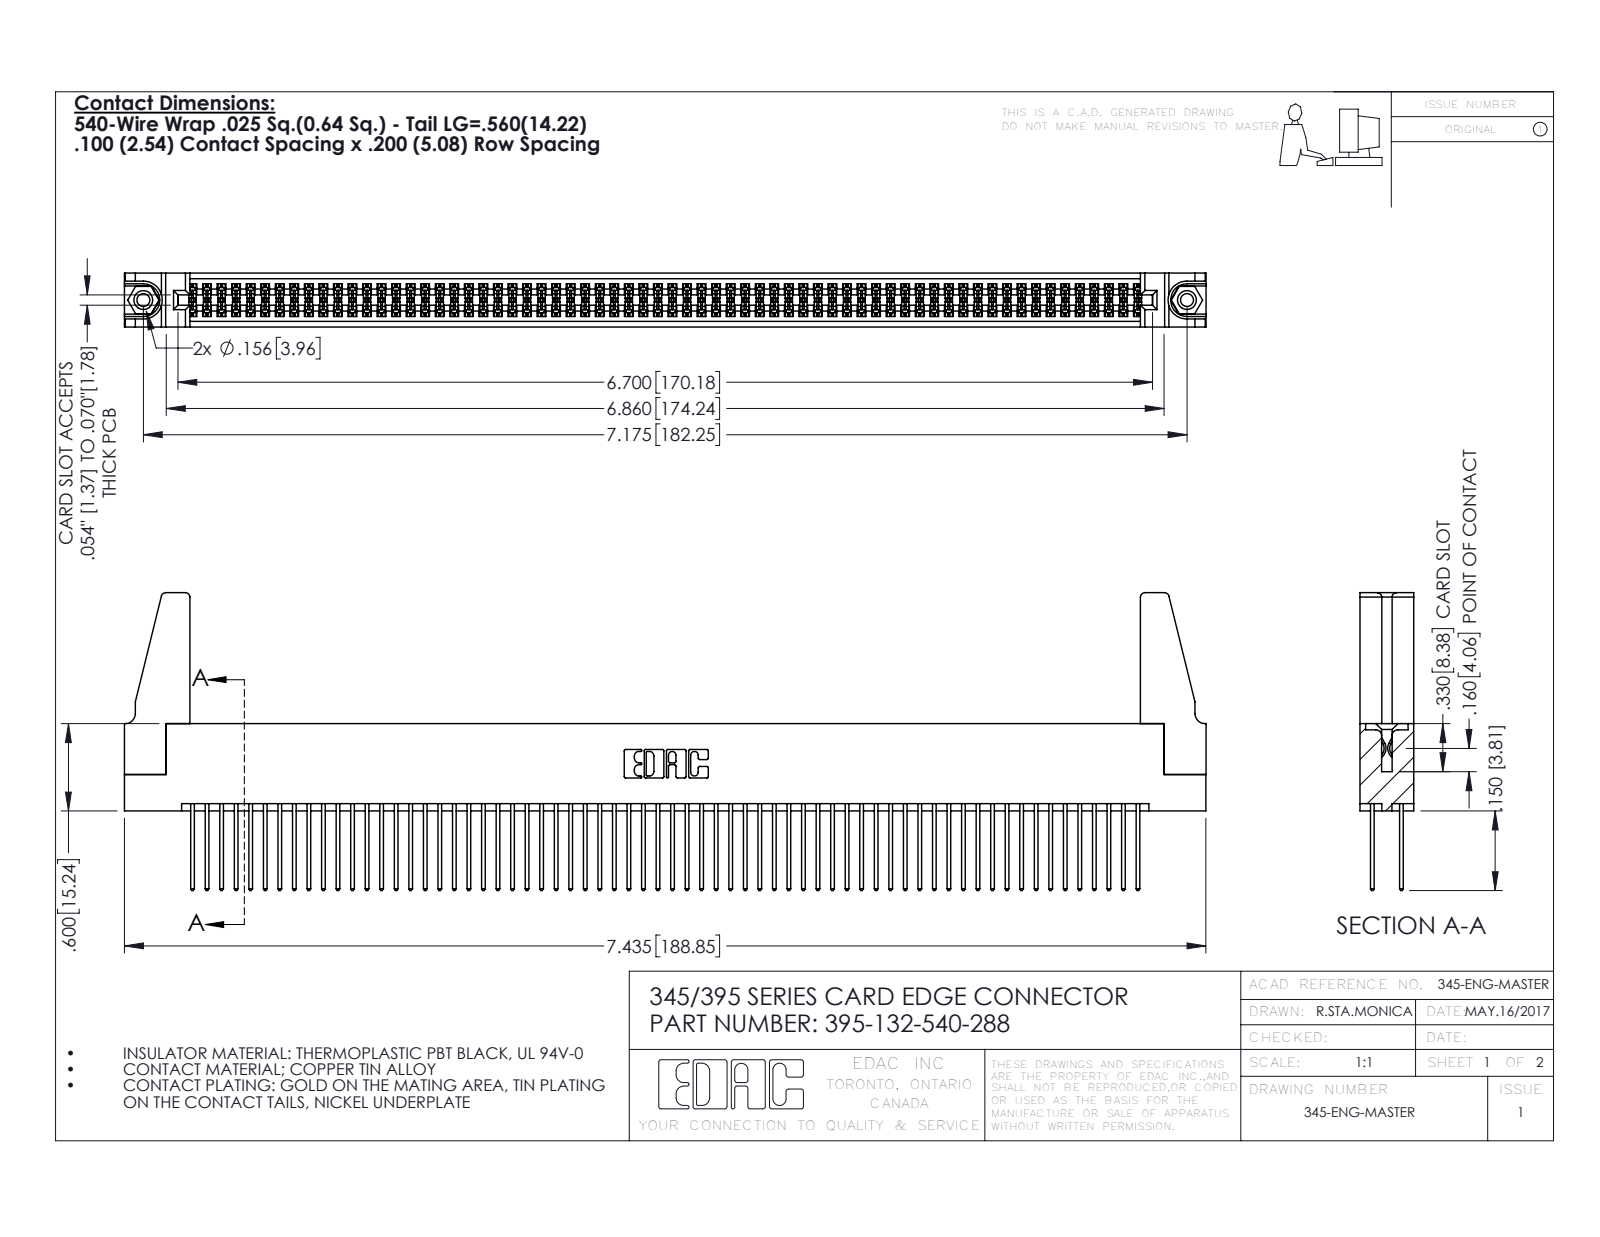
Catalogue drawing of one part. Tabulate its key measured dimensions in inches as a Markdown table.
| quantity | value |
| --- | --- |
| part name | 395-132-540-288; 345-220-078_345-220-088; 345-292-001_345-293-140; 345 Part_Flush Mounting Lugs - 0.156 Dia-TH (+1 more) |
| STEP written by | SolidWorks 2016 (CONFIG_CONTROL_DESIGN) |
| units | inches |
| bodies | 137 solids, 6850 faces (4508 planar, 2326 cylindrical, 16 other) |
| overall size | 7.436 × 2.047 × 0.37 |
| volume | 1.362 in³ |
| surface area | 52.85 in² |
| round holes (diameter × count) | 0.089 × 2, 0.125 × 2, 0.156 × 2, 0.064 × 1 |
| round bosses / shafts (diameter × count) | 0.155 × 2 |
| partial cylindrical surfaces (radius × count) | 0.006 × 198, 0.01 × 132, 0.01 × 22, 0.03 × 8, 0.007 × 6, 0.031 × 6, 0.026 × 3, 0.014 × 2 |
| main face-to-face distances | 0.072, 0.298, 0.2, 0.098, 0.272, 0.025, 0.37, 0.225, 0.175, 0.149 |
| hole center spacings | 0.27, 6.939, 7.175 |
